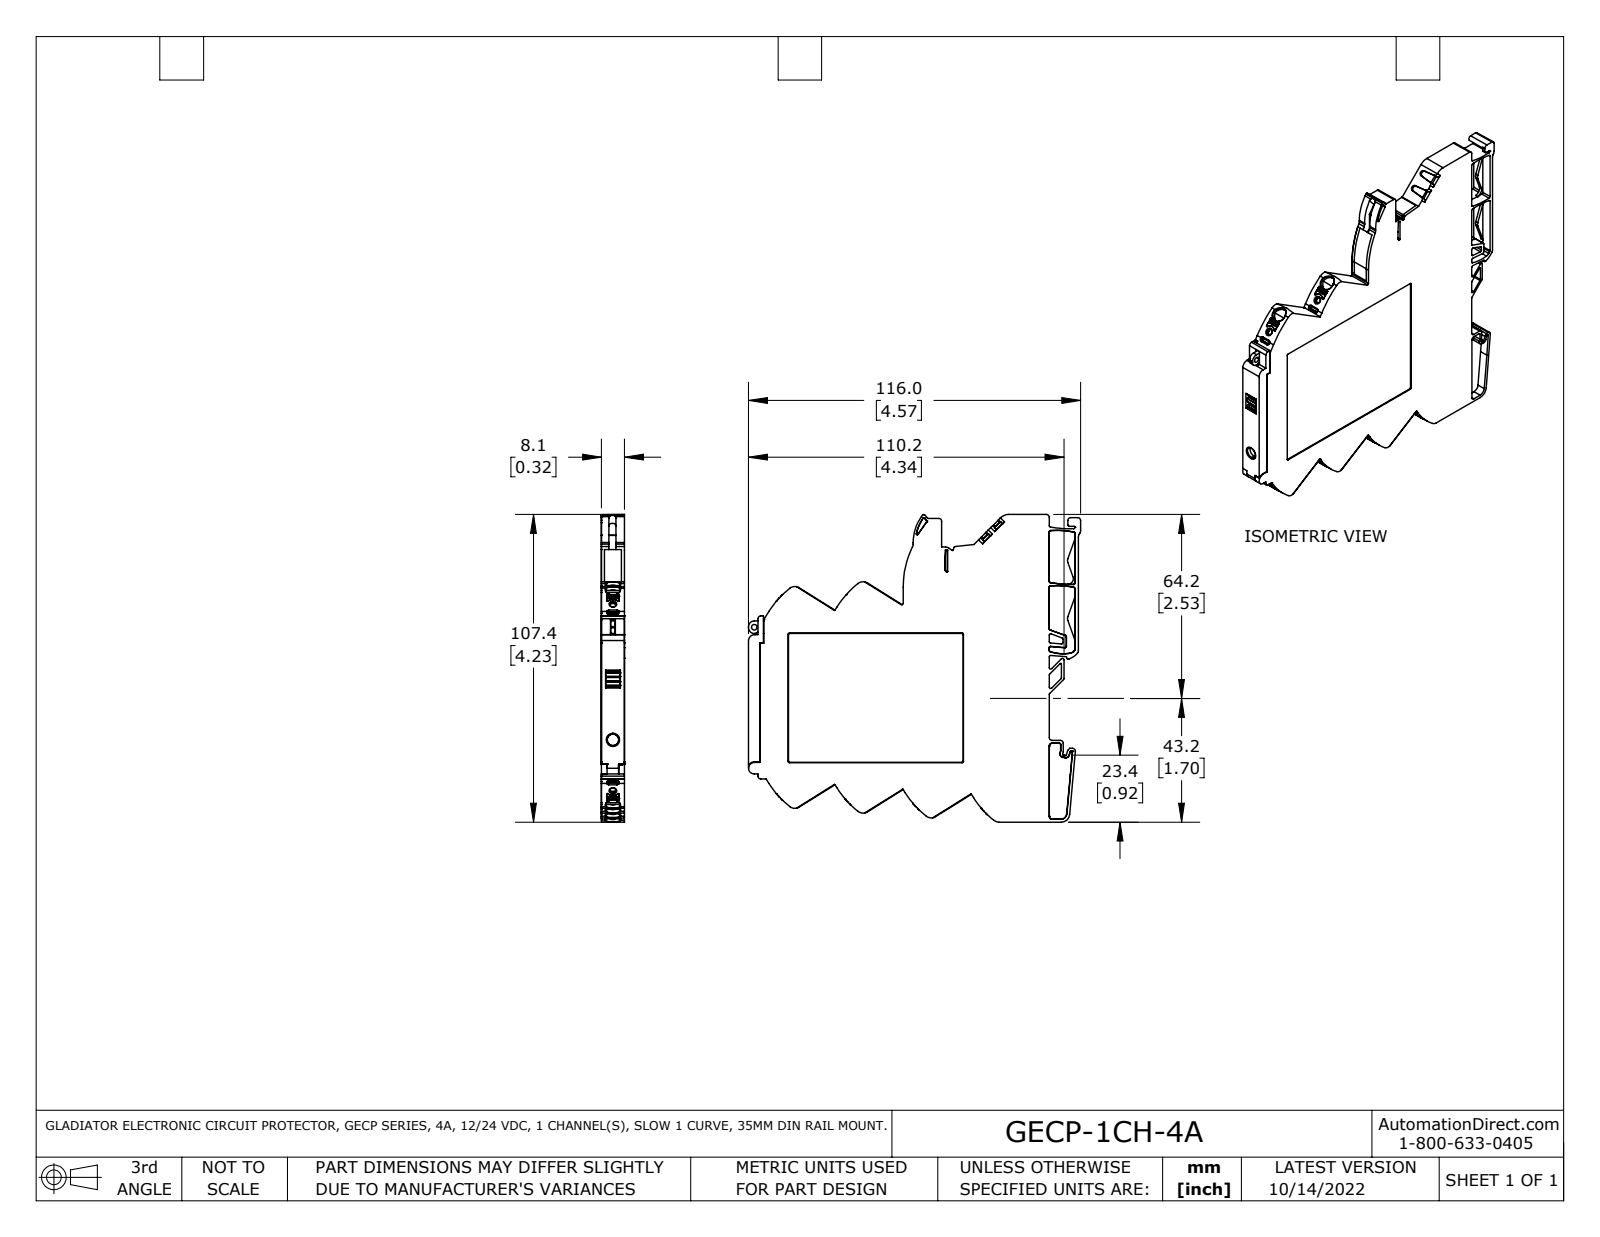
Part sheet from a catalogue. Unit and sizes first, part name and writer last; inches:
Units: inches
Overall size (bounding box): 4.567 × 4.241 × 0.319
Round holes (diameter × count): ⌀0.083 ×6, ⌀0.078 ×1, ⌀0.087 ×1
Round bosses / shafts (diameter × count): ⌀0.083 ×1
Partial cylindrical surfaces — rounded edges, fillets, slot ends (radius × count): R0.02 ×58, R0.039 ×45, R0.008 ×43, R0.01 ×28, R0.012 ×27, R0.079 ×13, R0.009 ×12, R1.299 ×12
Main face-to-face distances: 0.319, 0.311, 0.309, 0.317, 0.201, 0.157, 0.118, 0.354, 3.935, 4.093
Hole centre spacings: 0.559, 1.118, 0.559, 1.677, 1.937
Volume: 4.341 in³ · Surface area: 46.72 in²
Bodies: 1 solid, 1109 faces (549 planar, 405 cylindrical, 155 other)
Part name (STEP PRODUCT): GECP-1CH-4A
STEP written by: SolidWorks 2021 (AUTOMOTIVE_DESIGN)
